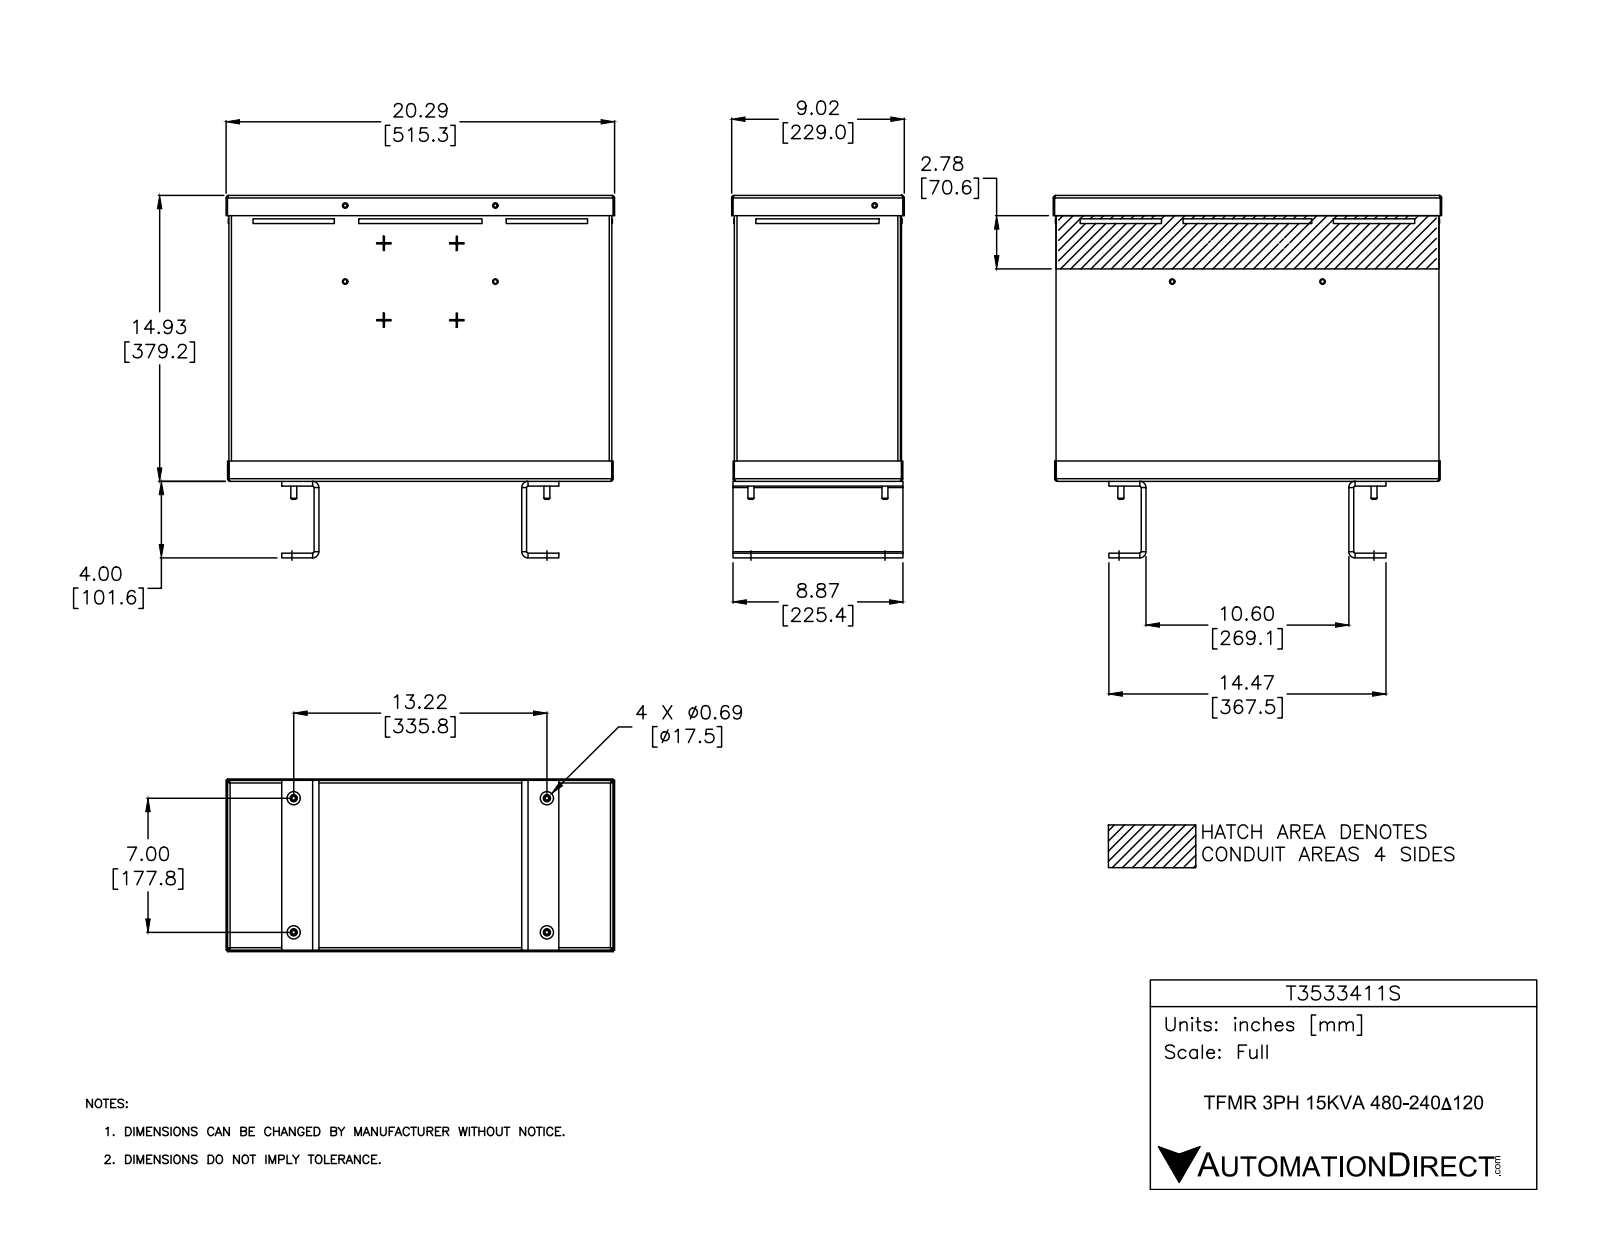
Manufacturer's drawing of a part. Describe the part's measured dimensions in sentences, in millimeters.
The part is named "T3533411S". Its 3-D file was written by "SolidWorks 2015 (AUTOMOTIVE_DESIGN)". It is 12 solids with 474 faces: 312 planar, 122 cylindrical and 40 other. Overall it measures 515.3 by 480.8 by 229 millimeters. Its volume is 1 875 000 cubic millimeters and its surface area 1 977 000 square millimeters. Round holes: 8 of diameter 7.1, 5 of diameter 4.7, 4 of diameter 8, 4 of diameter 9.5, 4 of diameter 17.4, 2 of diameter 5.3. Round bosses or shafts: 4 of diameter 7.9. Partial cylindrical surfaces (rounded edges, fillets, slot ends): 18 of radius 1.9, 14 of radius 3.4, 4 of radius 2.4, 4 of radius 3.1, 4 of radius 8.3. The main face-to-face distances are 1.5, 220.2, 377.7, 218.7, 221.7, 506.5, 379.2, 376.1, 508, 505. The hole center spacings are 100.8, 100.8, 125.9, 177.8, 199.2, 223.3, 262.2, 301.7.
